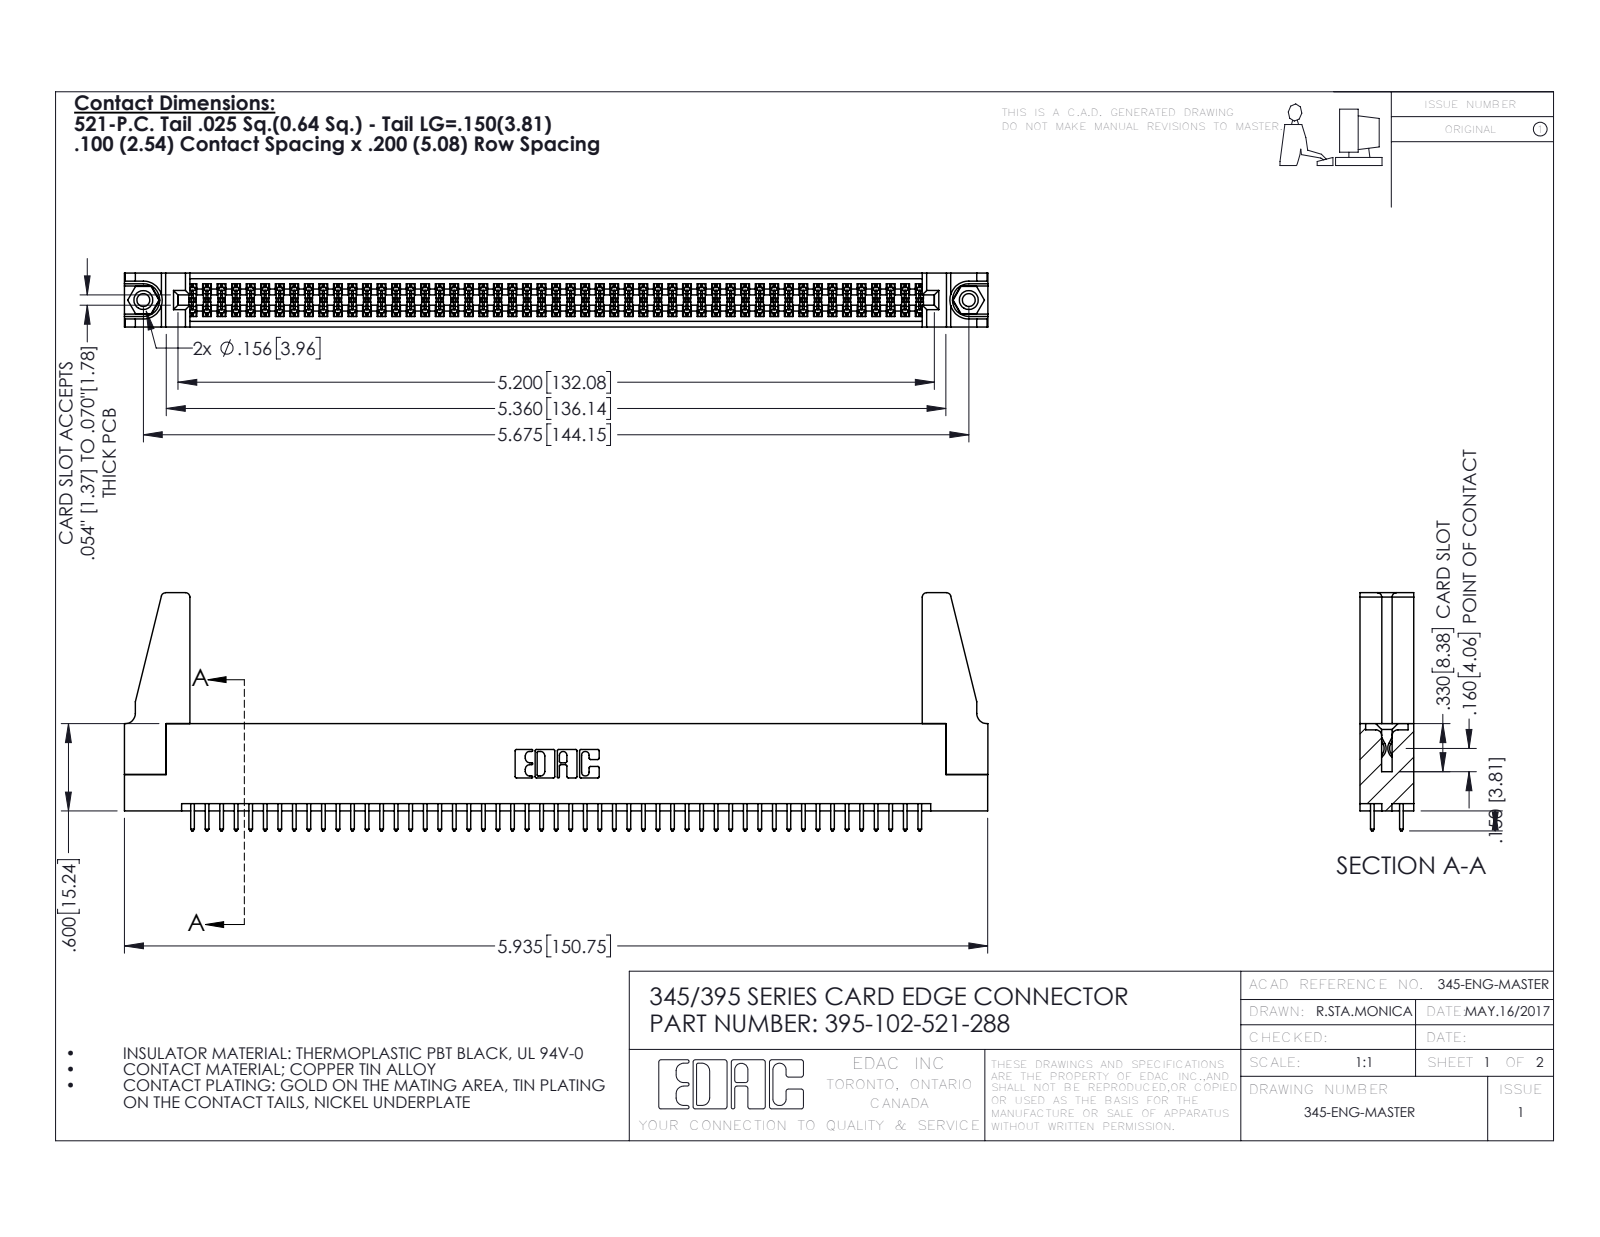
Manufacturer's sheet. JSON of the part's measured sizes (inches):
{"part_name": "345 Part_Flush Mounting Lugs - 0.156 Dia-TH; 345-250-001_345-250-001-102; 395-102-521-288; 345-292-001_345-293-121 (+1 more)", "step_written_by": "SolidWorks 2016 (CONFIG_CONTROL_DESIGN)", "units": "inches", "bodies": {"solids": 107, "faces": 5350, "planar": 3518, "cylindrical": 1816, "other": 16}, "overall_size": [5.936, 1.637, 0.37], "volume_in3": 1.095, "surface_area_in2": 38.34, "round_holes": [[0.089, 2], [0.125, 2], [0.156, 2], [0.064, 1]], "round_bosses_or_shafts": [[0.155, 2]], "partial_cylinders_radius": [[0.006, 153], [0.01, 102], [0.01, 22], [0.03, 8], [0.007, 6], [0.031, 6], [0.026, 3], [0.014, 2]], "face_to_face_distances": [0.072, 0.298, 0.37, 0.2, 0.098, 0.272, 0.025, 0.225, 0.175, 0.149], "hole_center_spacings": [0.27, 5.439, 5.675]}
